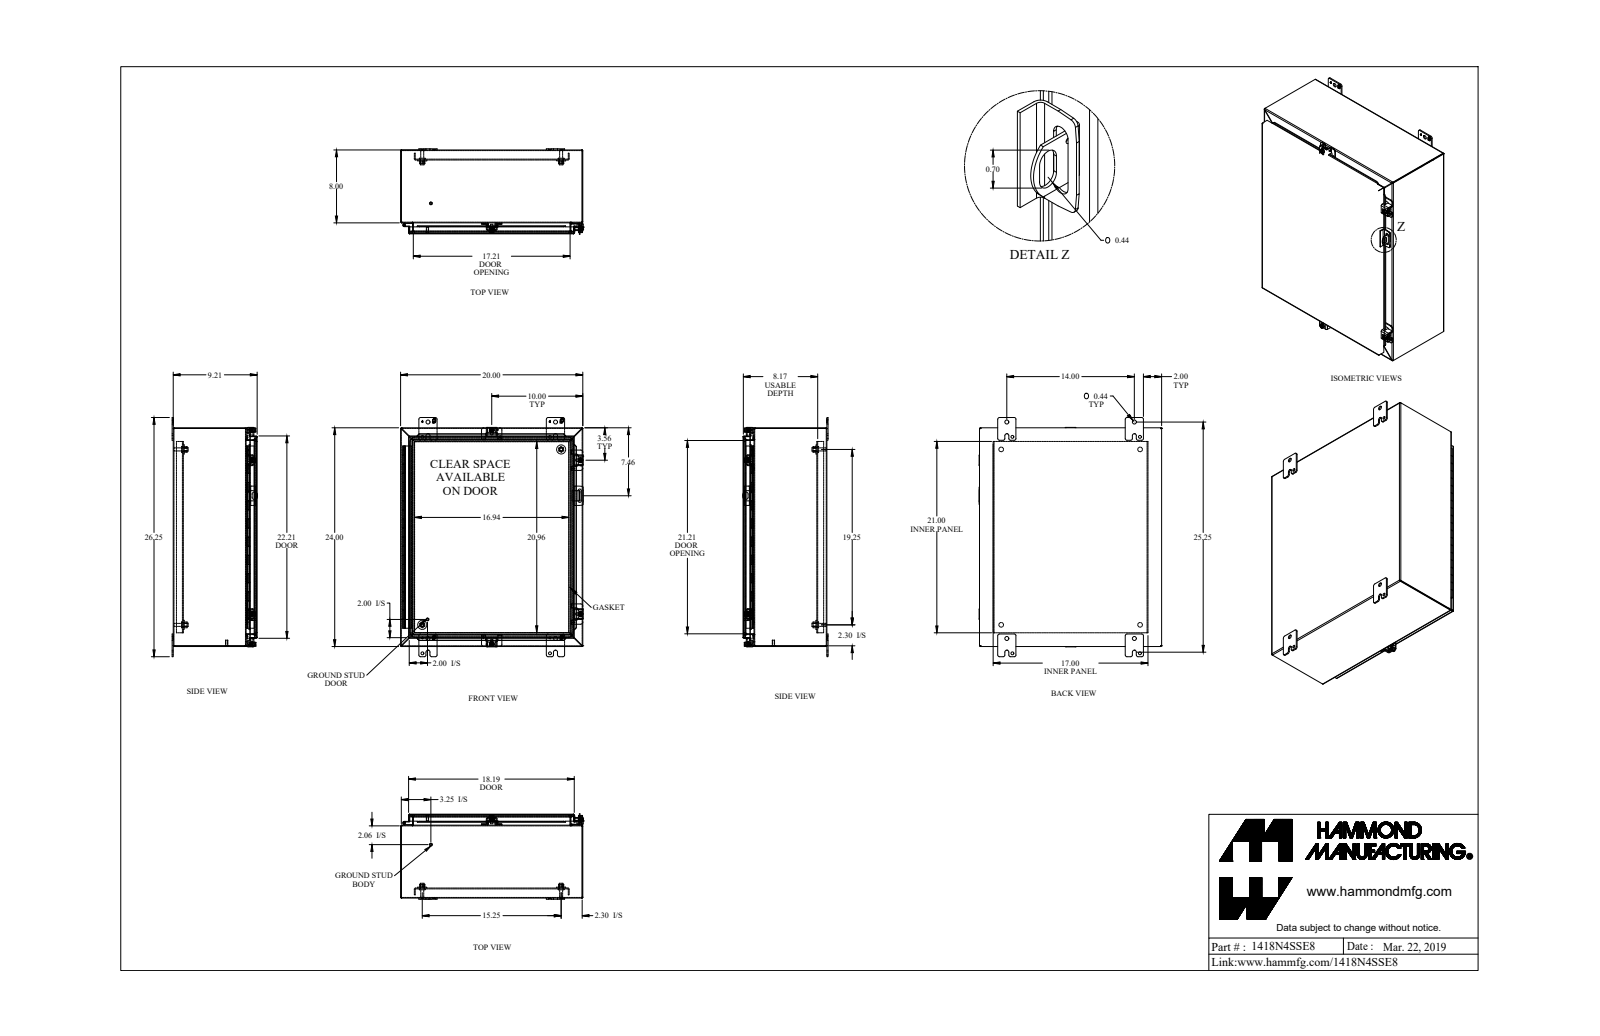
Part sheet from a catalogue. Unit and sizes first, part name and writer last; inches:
Units: inches
Overall size (bounding box): 26.25 × 20.063 × 9.375
Round holes (diameter × count): ⌀0.213 ×4, ⌀0.313 ×4, ⌀0.375 ×4, ⌀0.437 ×4, ⌀0.5 ×4, ⌀0.265 ×2, ⌀0.265 ×2, ⌀0.307 ×2, ⌀0.445 ×2, ⌀0.125 ×1, ⌀0.187 ×1
Round bosses / shafts (diameter × count): ⌀0.65 ×4, ⌀0.5 ×4, ⌀0.39 ×4, ⌀0.375 ×4, ⌀0.332 ×4, ⌀0.244 ×4, ⌀1 ×2, ⌀0.313 ×2
Partial cylindrical surfaces — rounded edges, fillets, slot ends (radius × count): R0.188 ×26, R0.036 ×24, R0.108 ×24, R0.048 ×21, R0.143 ×21, R0.25 ×20, R0.125 ×10, R0.045 ×8
Main face-to-face distances: 0.072, 9.066, 9.138, 0.072, 9.138, 9.21, 0.095, 0.937, 19.928, 1.009
Hole centre spacings: 7.916, 22.694, 14, 24.559, 1.735, 2.434, 14.702, 15.25
Volume: 184.8 in³ · Surface area: 4 870 in²
Bodies: 39 solids, 1499 faces (925 planar, 481 cylindrical, 93 other)
Part name (STEP PRODUCT): 1418N4SSE8_Default
STEP written by: SolidWorks 2019 (CONFIG_CONTROL_DESIGN)
